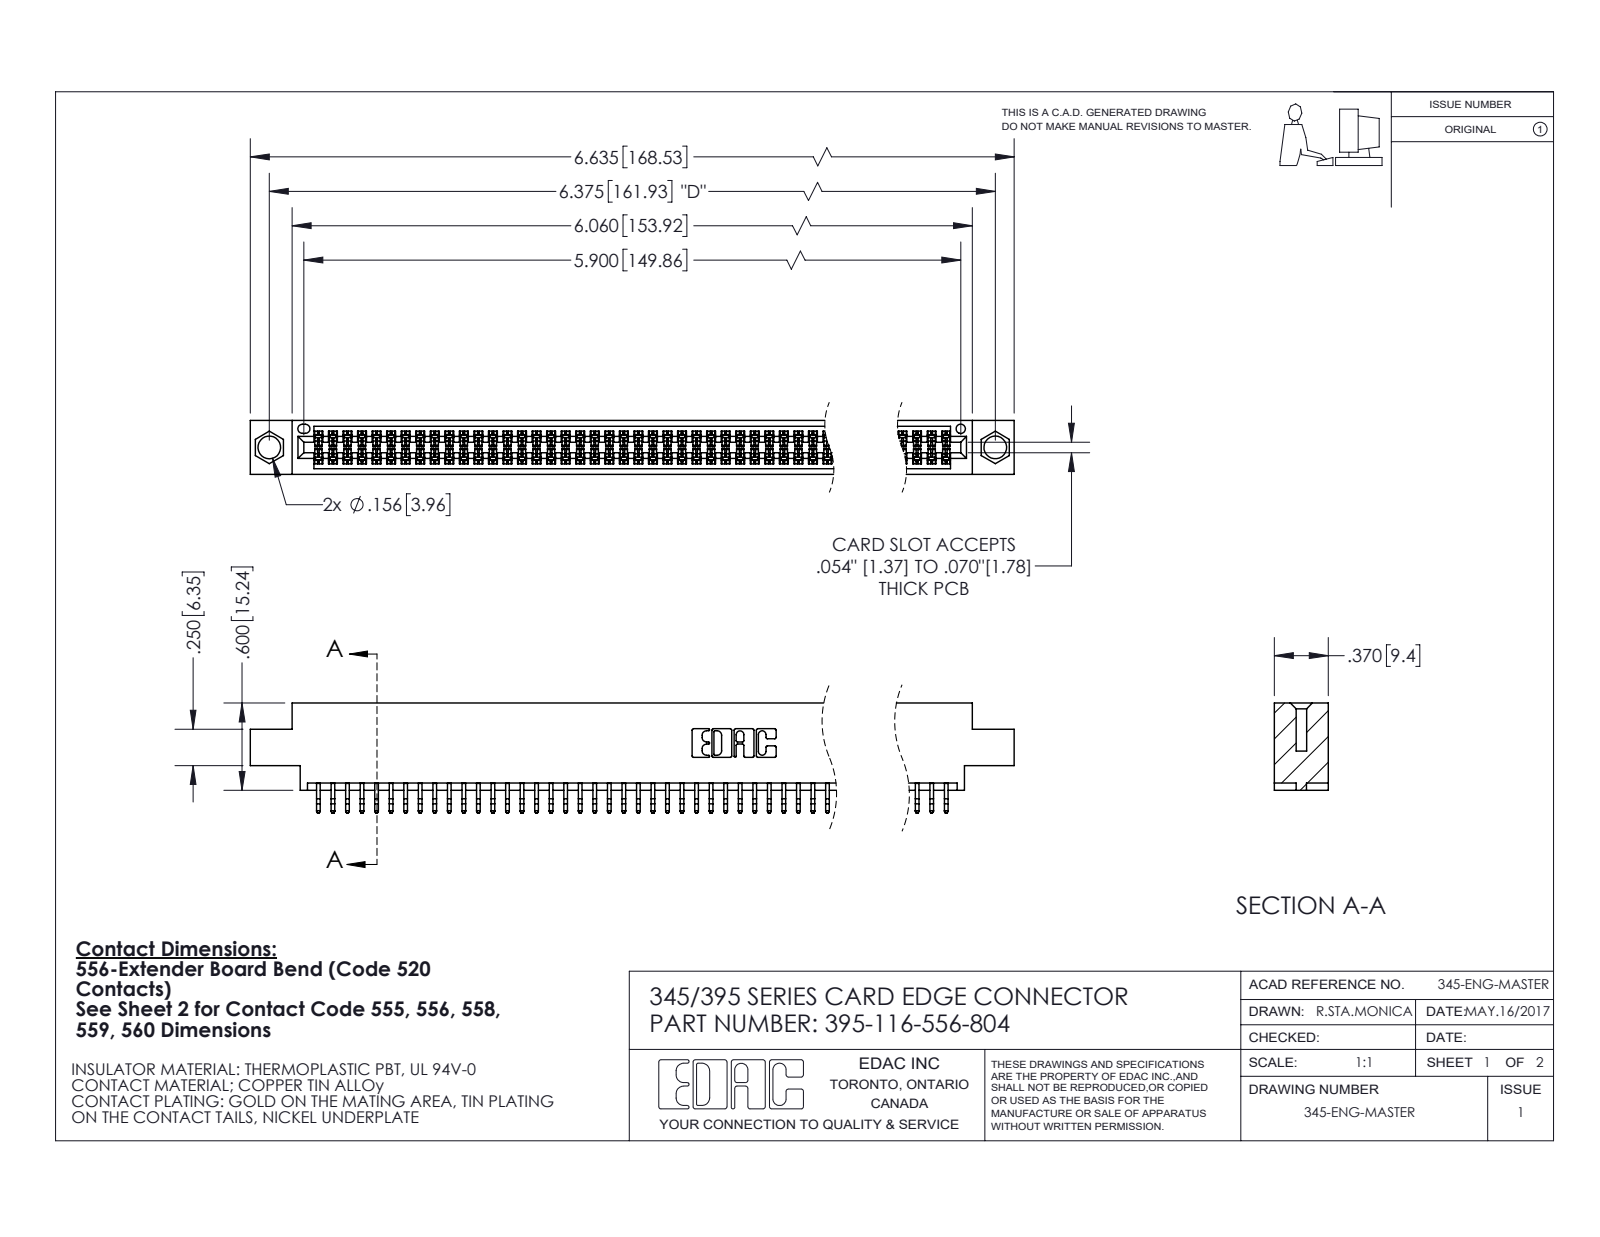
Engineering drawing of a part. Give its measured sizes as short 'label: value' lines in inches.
name: 395-116-556-804; 345 Part_0.170 Offset - 0.156 Dia-TI; 345-292-001_556 Tail
written by: SolidWorks 2020 (CONFIG_CONTROL_DESIGN)
unit: in
bodies: 117 solids, 6640 faces (4390 planar, 2250 cylindrical, 0 other)
size: 6.635 × 0.757 × 0.37
volume: 0.994 in³; area: 37.65 in²
holes: 2× ⌀0.156, 1× ⌀0.064
rounds: 232× R0.006, 22× R0.01, 6× R0.007, 6× R0.031, 3× R0.026, 2× R0.01, 2× R0.014, 2× R0.019
face distances: 0.072, 0.298, 0.37, 0.2, 0.025, 0.098, 0.272, 0.225, 0.175, 0.149
hole spacings: 0.27, 6.139, 6.375
